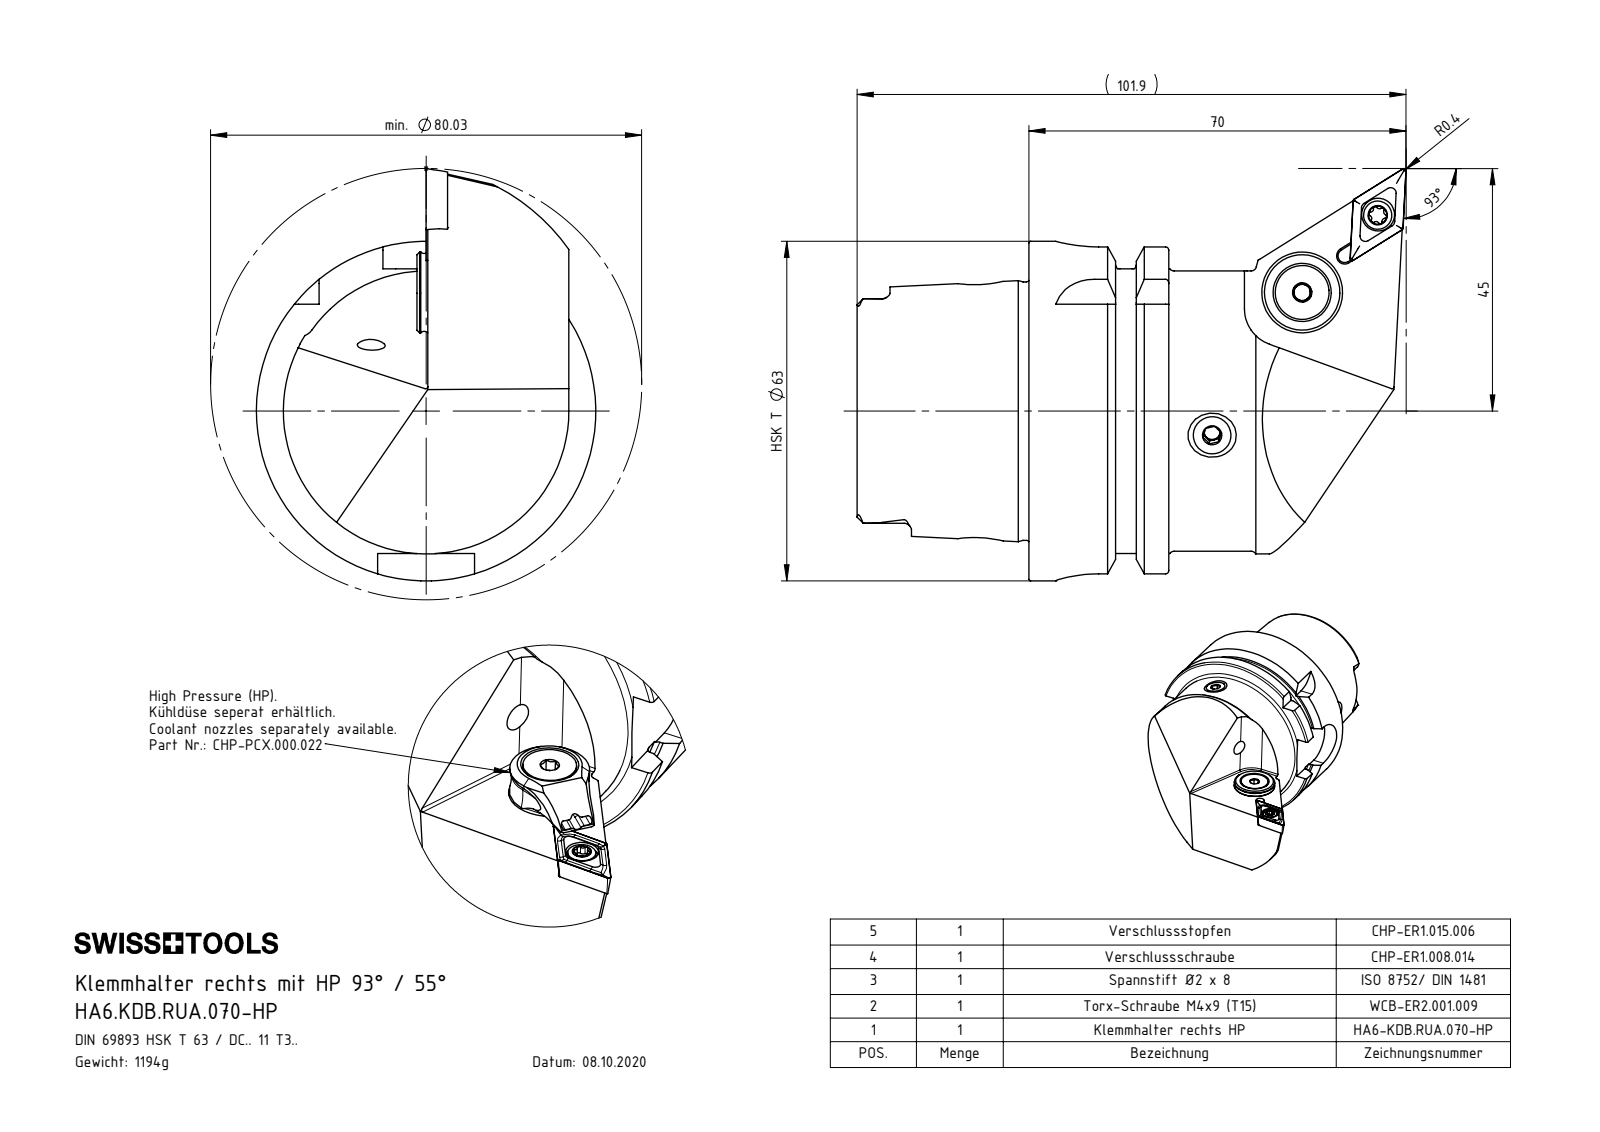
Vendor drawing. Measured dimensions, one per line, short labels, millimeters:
name: DIN 3771 - 13x1; HA6.KDB.RUA.070-HP; HA6-KDB.RUA.070-HP_A; CHP-ER1.008.014_A (+6 more)
written by: SolidWorks 2017 (AUTOMOTIVE_DESIGN)
unit: mm
bodies: 8 solids, 306 faces (118 planar, 75 cylindrical, 113 other)
size: 101.9 × 76.51 × 63
volume: 151 743 mm³; area: 33 276 mm²
holes: 2× ⌀4.2, 2× ⌀5, 1× ⌀1.2, 1× ⌀2, 1× ⌀2.5, 1× ⌀3, 1× ⌀3.3, 1× ⌀4.4, 1× ⌀5.2, 1× ⌀6.1, 1× ⌀7, 1× ⌀7.5
bosses: 1× ⌀63, 1× ⌀54.95, 1× ⌀52, 1× ⌀47.94, 1× ⌀15, 1× ⌀13.4, 1× ⌀10, 1× ⌀8
rounds: 6× R0.34, 6× R0.59, 6× R1.4, 4× R8, 2× R0.5, 2× R2.82, 2× R2.88, 2× R7
face distances: 25.95, 16, 9.95, 26.2, 31.9, 41.85, 57.85, 52.8, 21.8, 11.85
hole spacings: 4.5, 17.07, 17.18, 20.05, 20.17, 48.95, 51.19, 68.23
